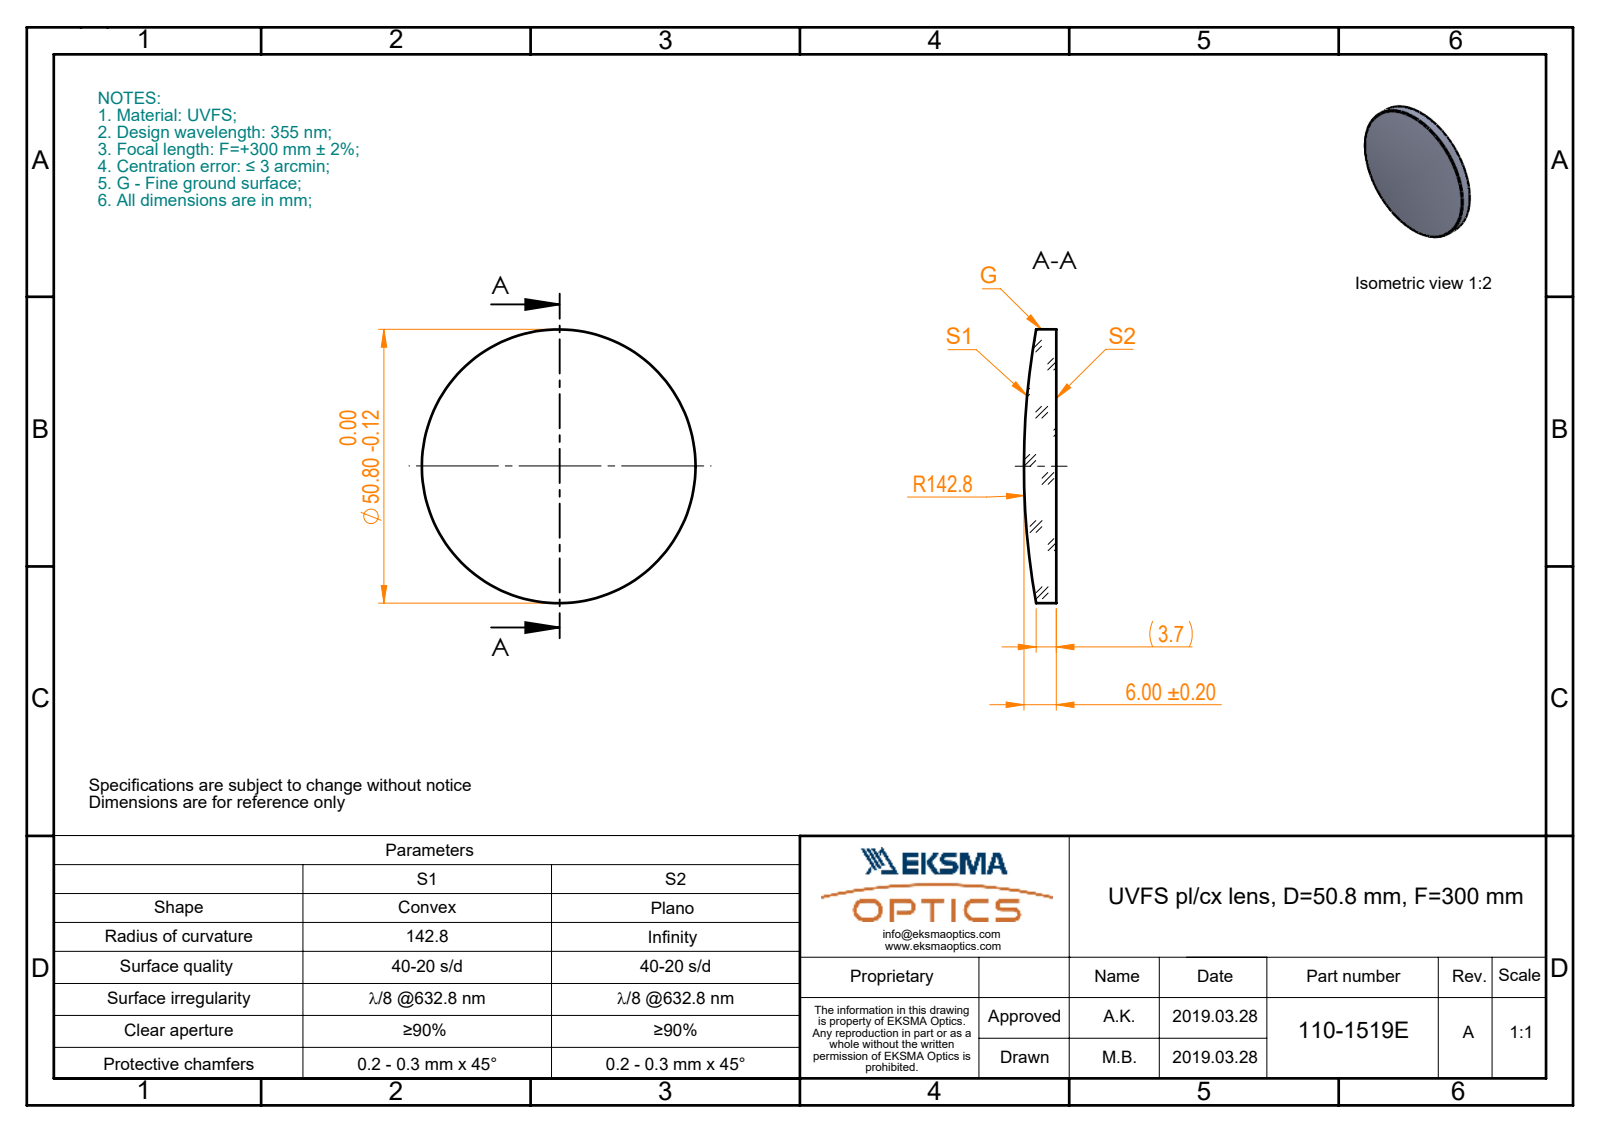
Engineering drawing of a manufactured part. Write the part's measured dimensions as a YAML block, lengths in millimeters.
part_name: "110-1519E UVFS pl-cx 50.8 F300"
step_written_by: "SolidWorks 2017 (CONFIG_CONTROL_DESIGN)"
units: millimeters
bodies: {solids: 1, faces: 5, planar: 1, cylindrical: 2, other: 2}
overall_size: [50.8, 50.8, 6]
volume: 9859
surface_area: 4664
round_bosses_or_shafts:
  - {diameter: 50.8, count: 1}
